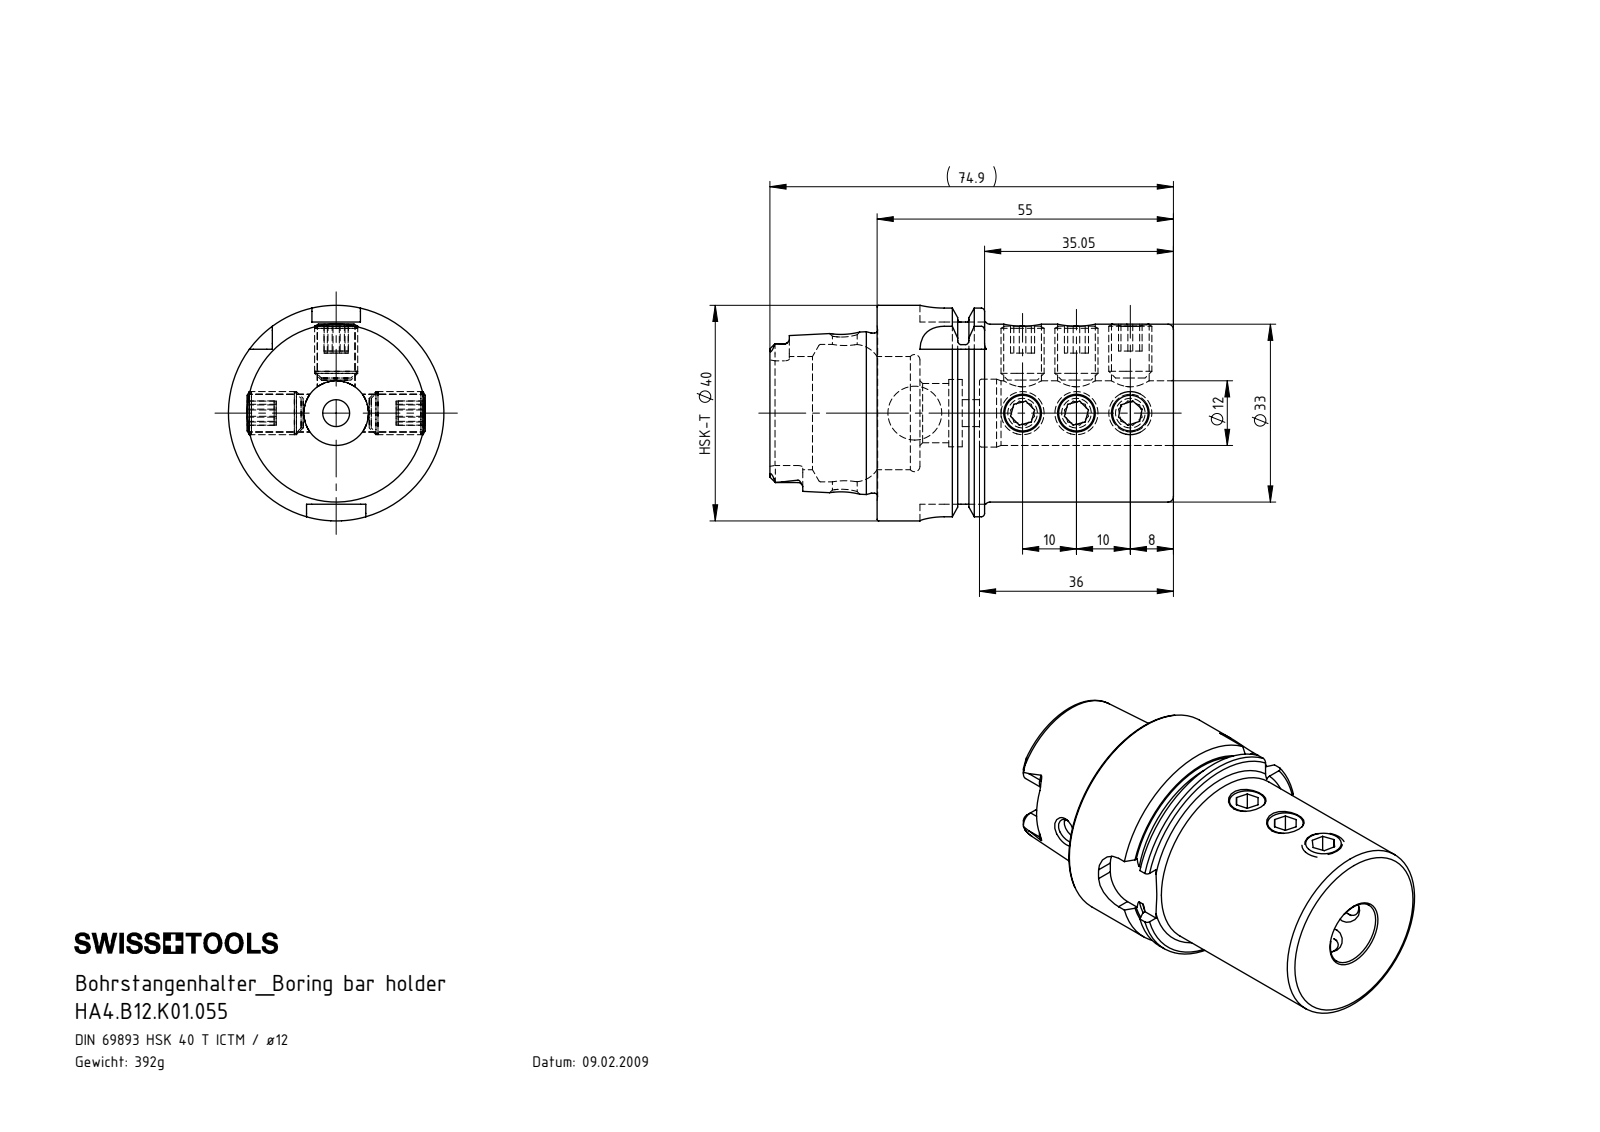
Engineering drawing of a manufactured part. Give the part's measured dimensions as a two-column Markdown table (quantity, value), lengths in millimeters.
| quantity | value |
| --- | --- |
| part name | HA4-B12.K01.055_C_Fertigbearbeitung; HA4.B12.K01.055; ISO 4026 - M8 x 10_PreviewCfg |
| STEP written by | SolidWorks 2017 (AUTOMOTIVE_DESIGN) |
| units | millimeters |
| bodies | 10 solids, 319 faces (128 planar, 86 cylindrical, 105 other) |
| overall size | 74.9 × 40 × 40 |
| volume | 49 956 mm³ |
| surface area | 19 427 mm² |
| round holes (diameter × count) | 7 × 6, 4.6 × 1, 5 × 1, 10 × 1, 11 × 1, 12 × 1, 12.5 × 1, 12.6 × 1, 21 × 1, 25.5 × 1 |
| round bosses / shafts (diameter × count) | 8 × 6, 40 × 1, 34.75 × 1, 33 × 1, 29.71 × 1 |
| partial cylindrical surfaces (radius × count) | 0.9 × 6, 1.88 × 4, 4.5 × 4 |
| main face-to-face distances | 55, 5, 4, 10, 7.95, 47.05, 19.95, 12, 35.05, 0.38 |
| hole center spacings | 10, 20, 30, 33, 40, 43, 53 |
